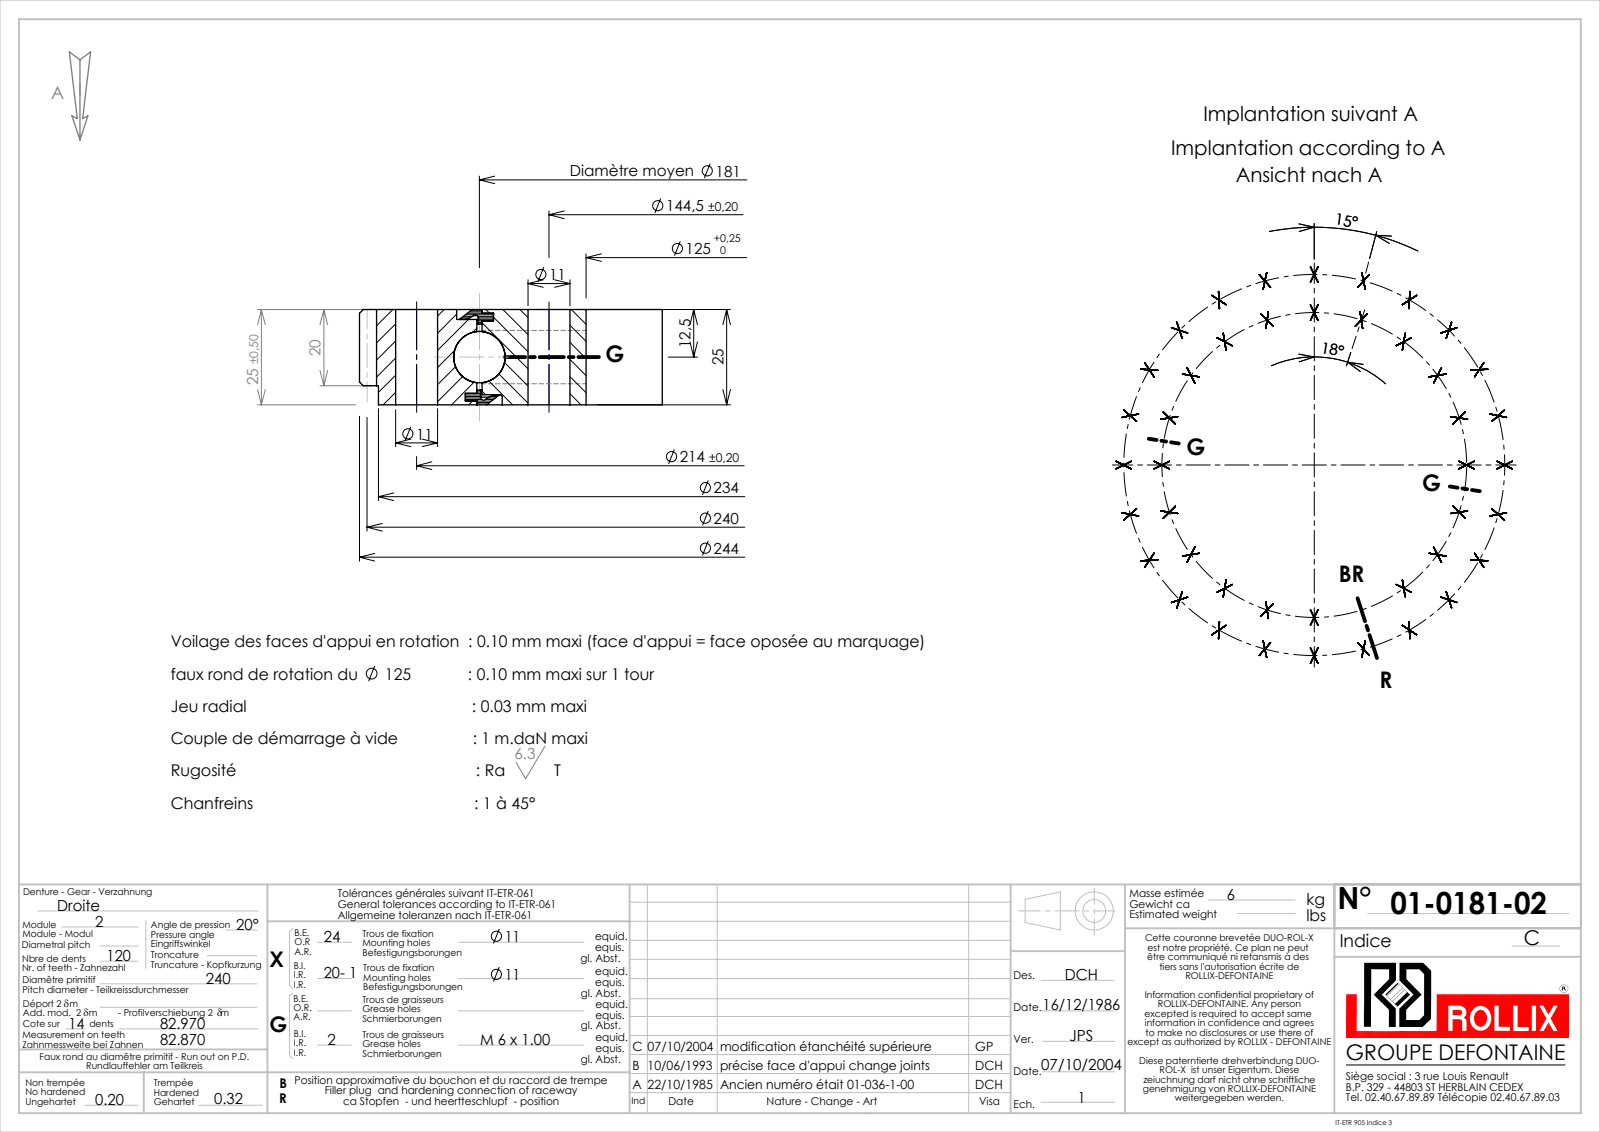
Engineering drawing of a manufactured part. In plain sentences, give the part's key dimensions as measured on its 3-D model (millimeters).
The part is named "01-0181-02". Its 3-D file was written by "SolidWorks 2016 (CONFIG_CONTROL_DESIGN)". It is 5 solids with 894 faces: 261 planar, 371 cylindrical and 262 other. Overall it measures 243.96 by 243.96 by 25 millimeters. Its volume is 614 750 cubic millimeters and its surface area 208 946 square millimeters. Round holes: 43 of diameter 11, 2 of diameter 5, 1 of diameter 125, 1 of diameter 173.65, 1 of diameter 180.35, 1 of diameter 182.35, 1 of diameter 188.35, 1 of diameter 192.95. Round bosses or shafts: 1 of diameter 234, 1 of diameter 181.65, 1 of diameter 179.65, 1 of diameter 169.05. Partial cylindrical surfaces (rounded edges, fillets, slot ends): 1 of radius 117.5, 1 of radius 122. The main face-to-face distances are 25, 2, 3, 22, 1, 24, 21, 19, 22.4, 2.6. The hole center spacings are 107, 81.89, 130.27, 169.77, 206.7, 212.16, 27.93, 55.39.
